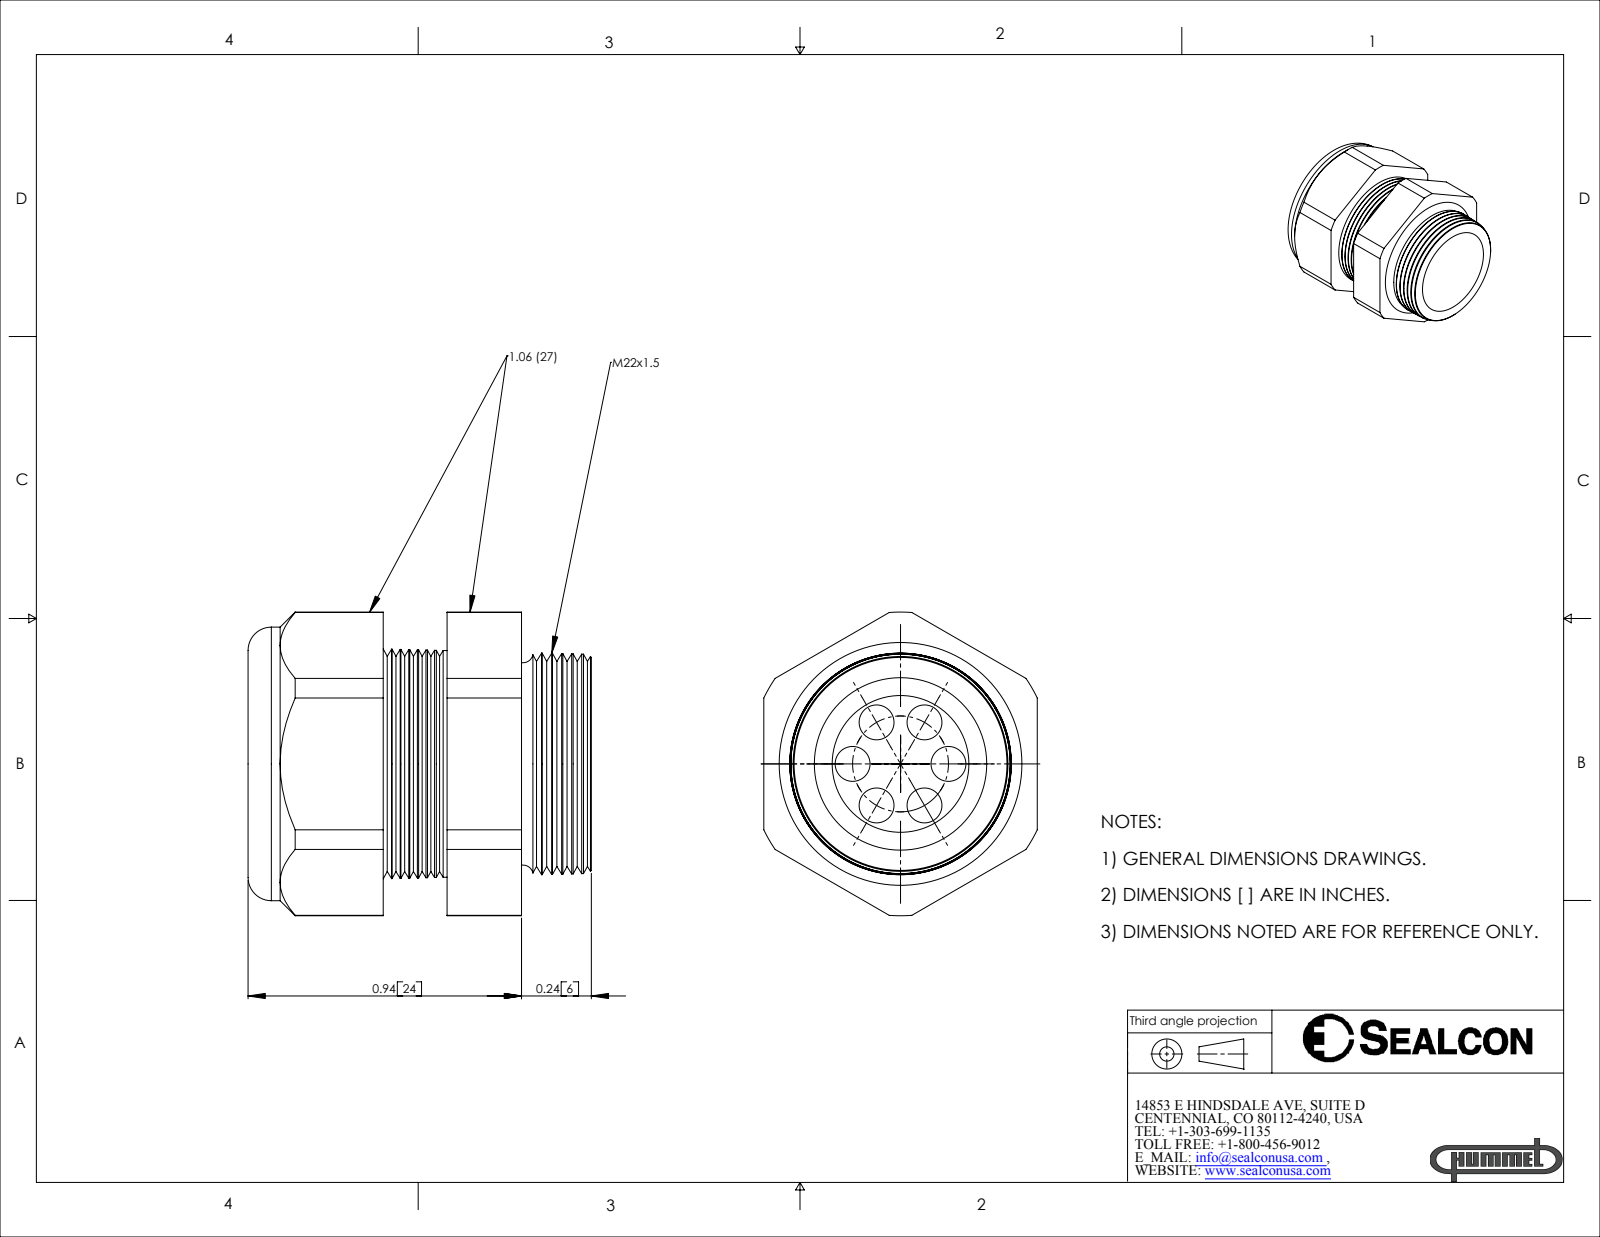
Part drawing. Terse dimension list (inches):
name: CD22M5-BR
written by: SolidWorks 2007 (CONFIG_CONTROL_DESIGN)
unit: in
bodies: 2 solids, 144 faces (20 planar, 32 cylindrical, 92 other)
size: 1.18 × 1.043 × 0.94
volume: 0.517 in³; area: 8.831 in²
holes: 6× ⌀0.12, 1× ⌀0.45, 1× ⌀0.47
bosses: 1× ⌀0.94
rounds: 1× R0.522
face distances: 0.94, 0.684, 0.465, 0.22, 0.476, 0.256, 1.18, 0.715, 0.496, 0.24
hole spacings: 0.165, 0.285, 0.329
